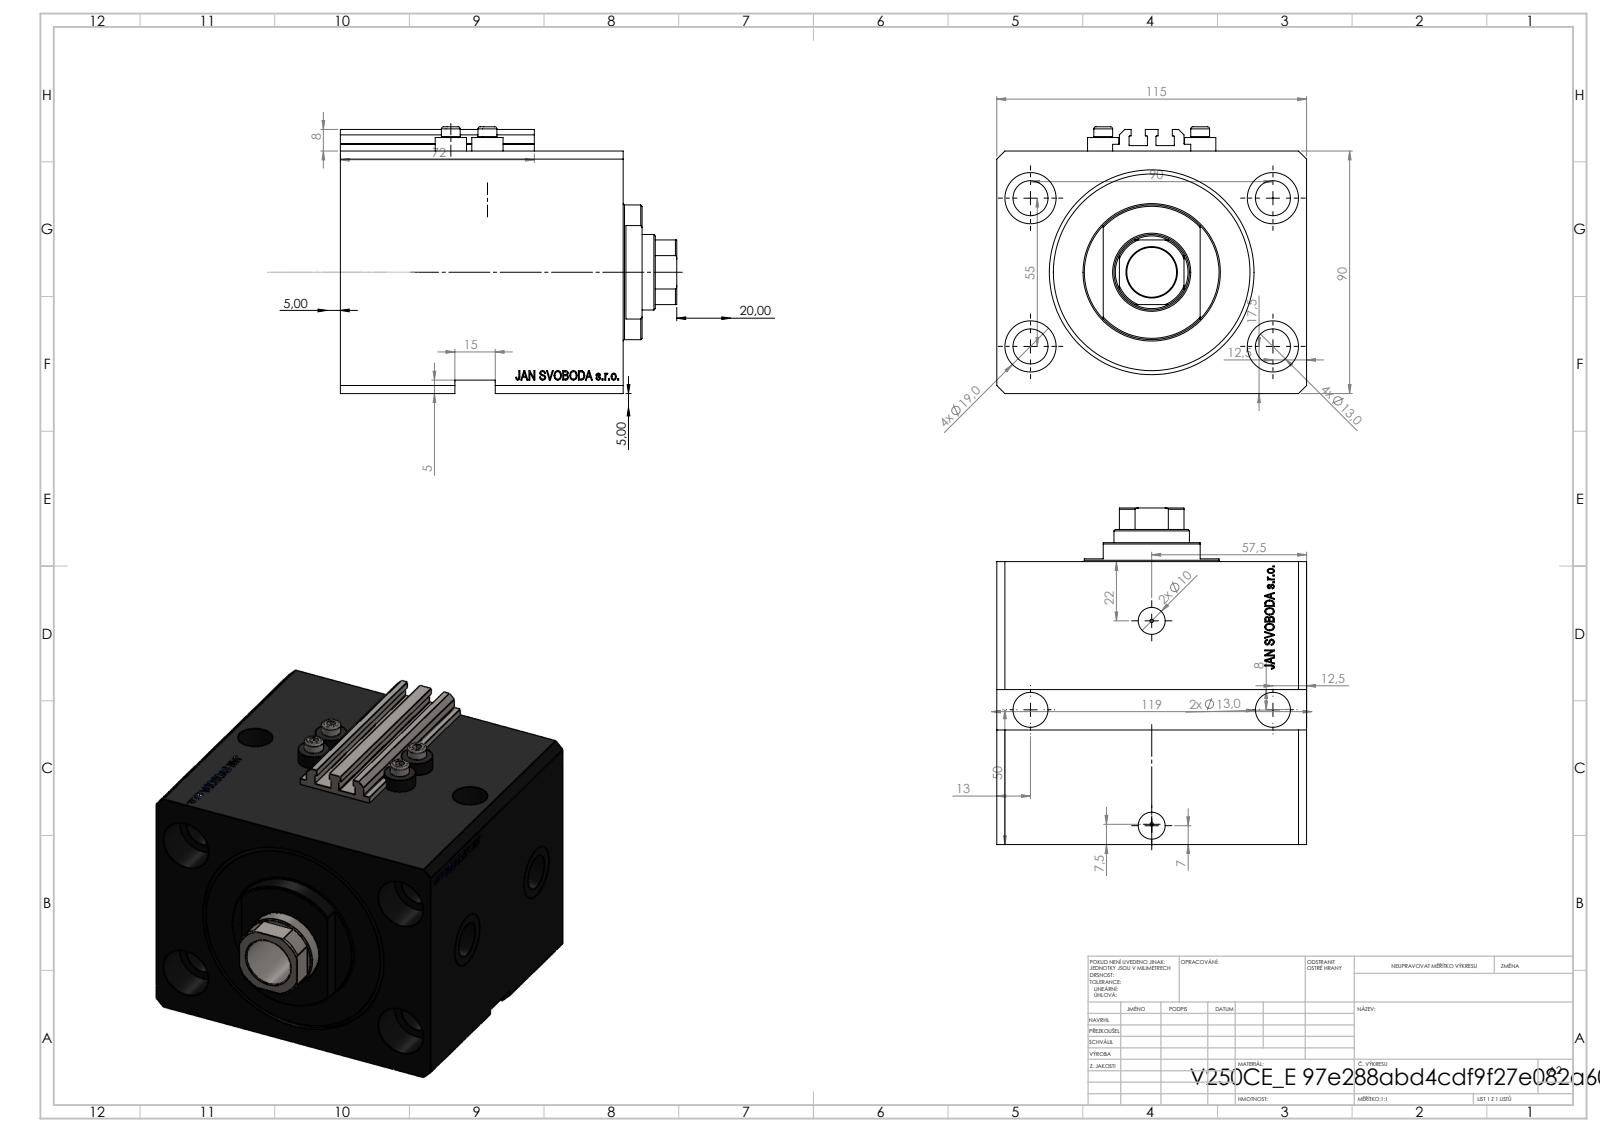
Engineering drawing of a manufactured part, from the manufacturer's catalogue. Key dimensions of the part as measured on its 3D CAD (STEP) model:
Part name (STEP PRODUCT): V250CE_VC_E; V250CE_E_Body; V250CE_C_VCP; ALLEN BOLT V250CE
STEP written by: SolidWorks 2019 (CONFIG_CONTROL_DESIGN)
Units: millimetres
Bodies: 8 solids, 1107 faces (543 planar, 126 cylindrical, 438 other)
Overall size (bounding box): 125 × 115 × 99
Volume: 954 568 mm³ · Surface area: 153 949 mm²
Round holes (diameter × count): ⌀13 ×6, ⌀1.25 ×4, ⌀4 ×4, ⌀19 ×4, ⌀10 ×2, ⌀13.16 ×2, ⌀20 ×2, ⌀18.5 ×1, ⌀28 ×1, ⌀63 ×1, ⌀76 ×1
Round bosses / shafts (diameter × count): ⌀11.6 ×4, ⌀7 ×4, ⌀50 ×1
Partial cylindrical surfaces — rounded edges, fillets, slot ends (radius × count): R0.2 ×10, R13.5 ×1
Main face-to-face distances: 90, 20, 115, 85, 105, 87.1, 17.9, 67.1, 40, 65
Hole centre spacings: 52.74, 55, 90, 13.6, 27.39, 28.46, 33.62, 36
